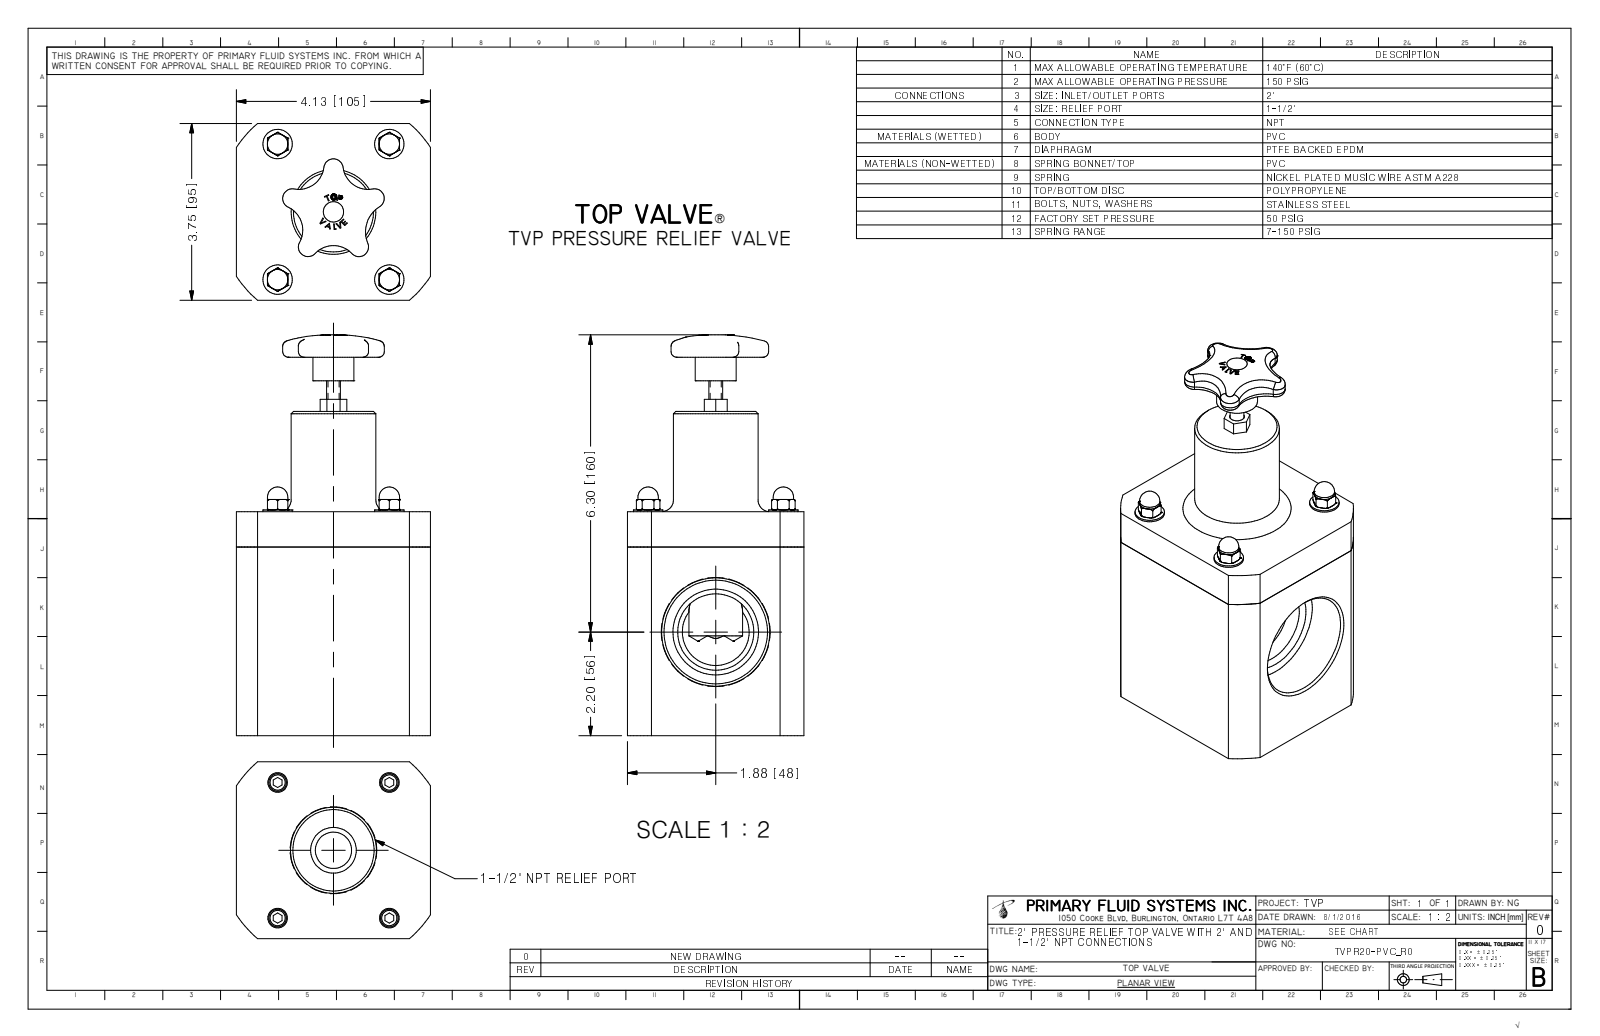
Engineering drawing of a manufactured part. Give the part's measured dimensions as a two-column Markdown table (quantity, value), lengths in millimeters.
| quantity | value |
| --- | --- |
| part name | TVPR20-PVC_R0 |
| STEP written by | Autodesk Inventor 2009 (AUTOMOTIVE_DESIGN) |
| units | millimeters |
| bodies | 1 solid, 340 faces (145 planar, 46 cylindrical, 149 other) |
| overall size | 215.9 × 104.8 × 95.3 |
| volume | 1 136 000 mm³ |
| surface area | 93 740 mm² |
| round holes (diameter × count) | 4.4 × 4, 43.9 × 1, 55.9 × 1 |
| round bosses / shafts (diameter × count) | 15.9 × 4, 11 × 4, 9.5 × 4, 45.7 × 1, 22.1 × 1, 7.4 × 1 |
| partial cylindrical surfaces (radius × count) | 2.2 × 5, 5.2 × 5, 13.6 × 4, 16.7 × 4, 15.9 × 1, 18.9 × 1, 62.9 × 1 |
| main face-to-face distances | 95.3, 22.9, 120.7, 104.8, 81.9, 59.1, 97.8, 174.6, 151.8, 54 |
| hole center spacings | 47.3, 47.4, 60.3, 73, 94.7 |
